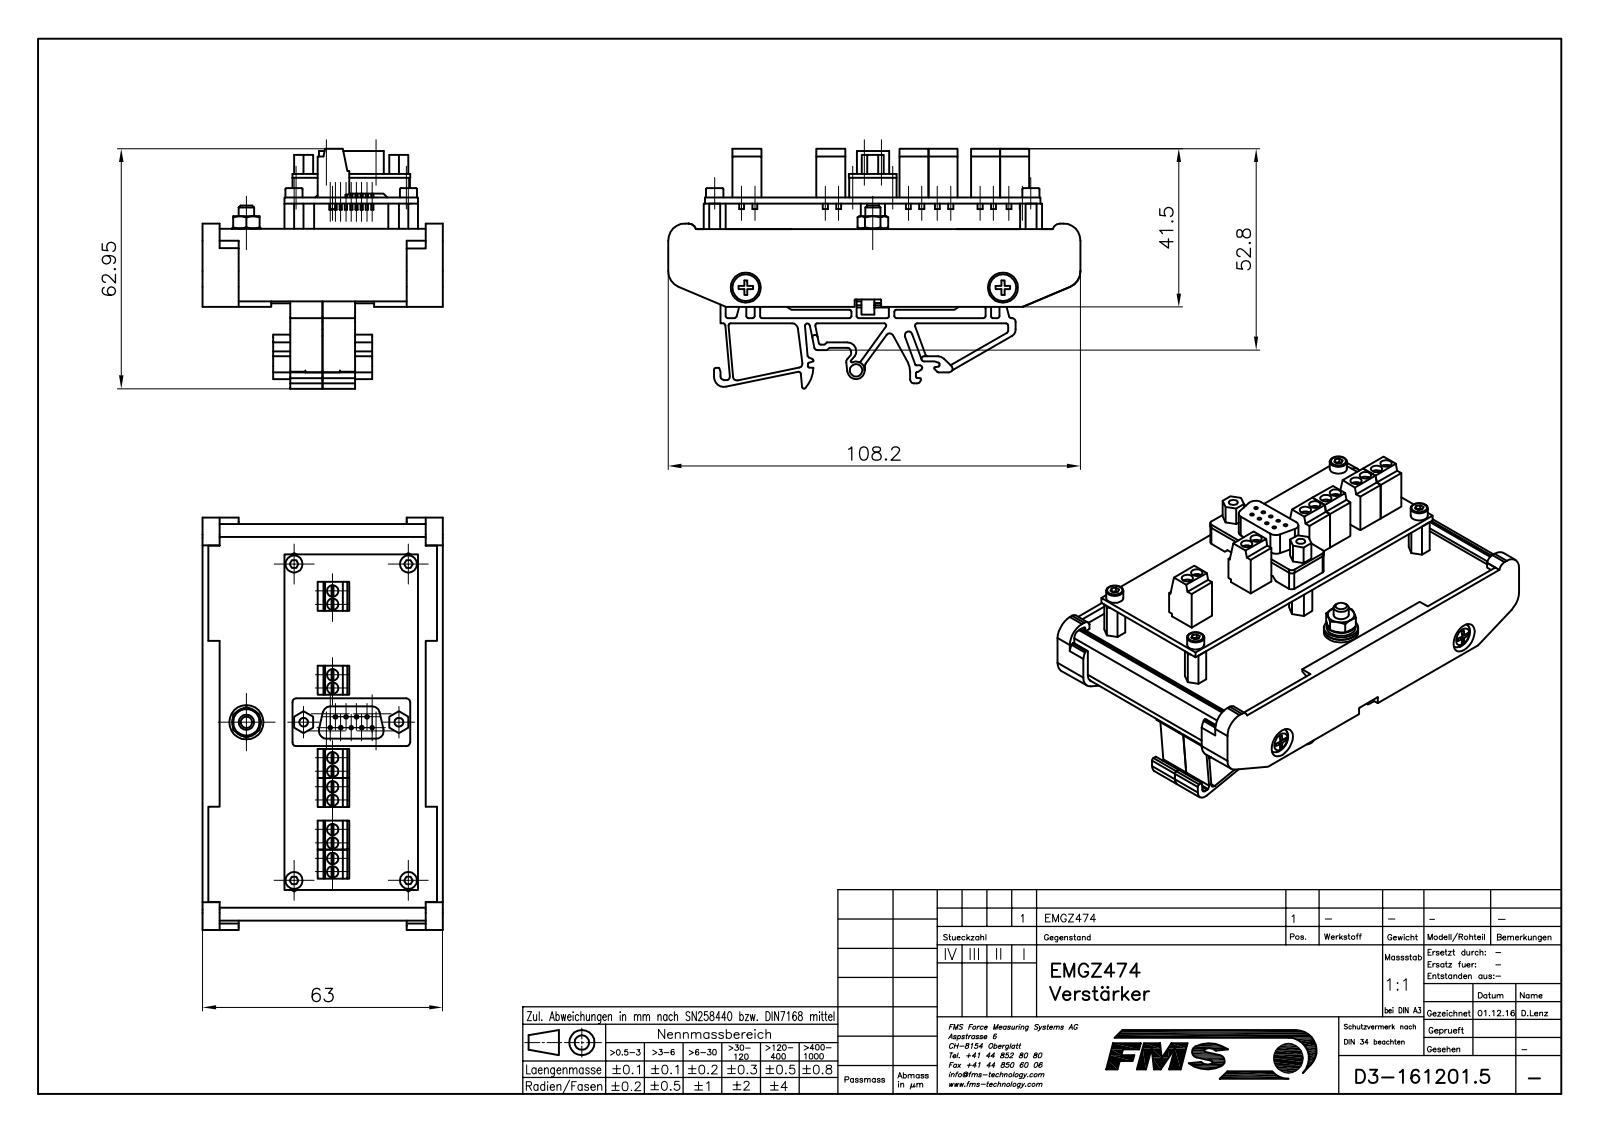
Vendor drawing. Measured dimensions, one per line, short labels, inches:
name: E1612015; E1612011; PF RS 100 OR 2000MM A.1 4144870000 100; E1612011|AVE_RENDER (+8 more)
written by: Mechanical Desktop 2009 (CONFIG_CONTROL_DESIGN)
unit: in
bodies: 43 solids, 1959 faces (1047 planar, 652 cylindrical, 260 other)
size: 4.26 × 2.48 × 2.478
volume: 4.213 in³; area: 125.9 in²
holes: 12× ⌀0.118, 9× ⌀0.039, 4× ⌀0.076, 4× ⌀0.106, 3× ⌀0.126, 2× ⌀0.091, 2× ⌀0.098, 2× ⌀0.177, 2× ⌀0.311, 1× ⌀0.13, 1× ⌀0.157, 1× ⌀0.161
bosses: 12× ⌀0.051, 9× ⌀0.024, 6× ⌀0.118, 4× ⌀0.177, 4× ⌀0.157, 4× ⌀0.098, 2× ⌀0.276, 2× ⌀0.094
rounds: 55× R0.039, 52× R0.02, 11× R0.012, 9× R0.079, 5× R0.028, 4× R0.008, 4× R0.037, 4× R0.11
face distances: 0.059, 0.654, 0.594, 0.098, 0.417, 1.071, 0.476, 0.063, 2.421, 1.008
hole spacings: 0.108, 0.138, 0.217, 0.124, 0.124, 0.299, 0.74, 1.637
